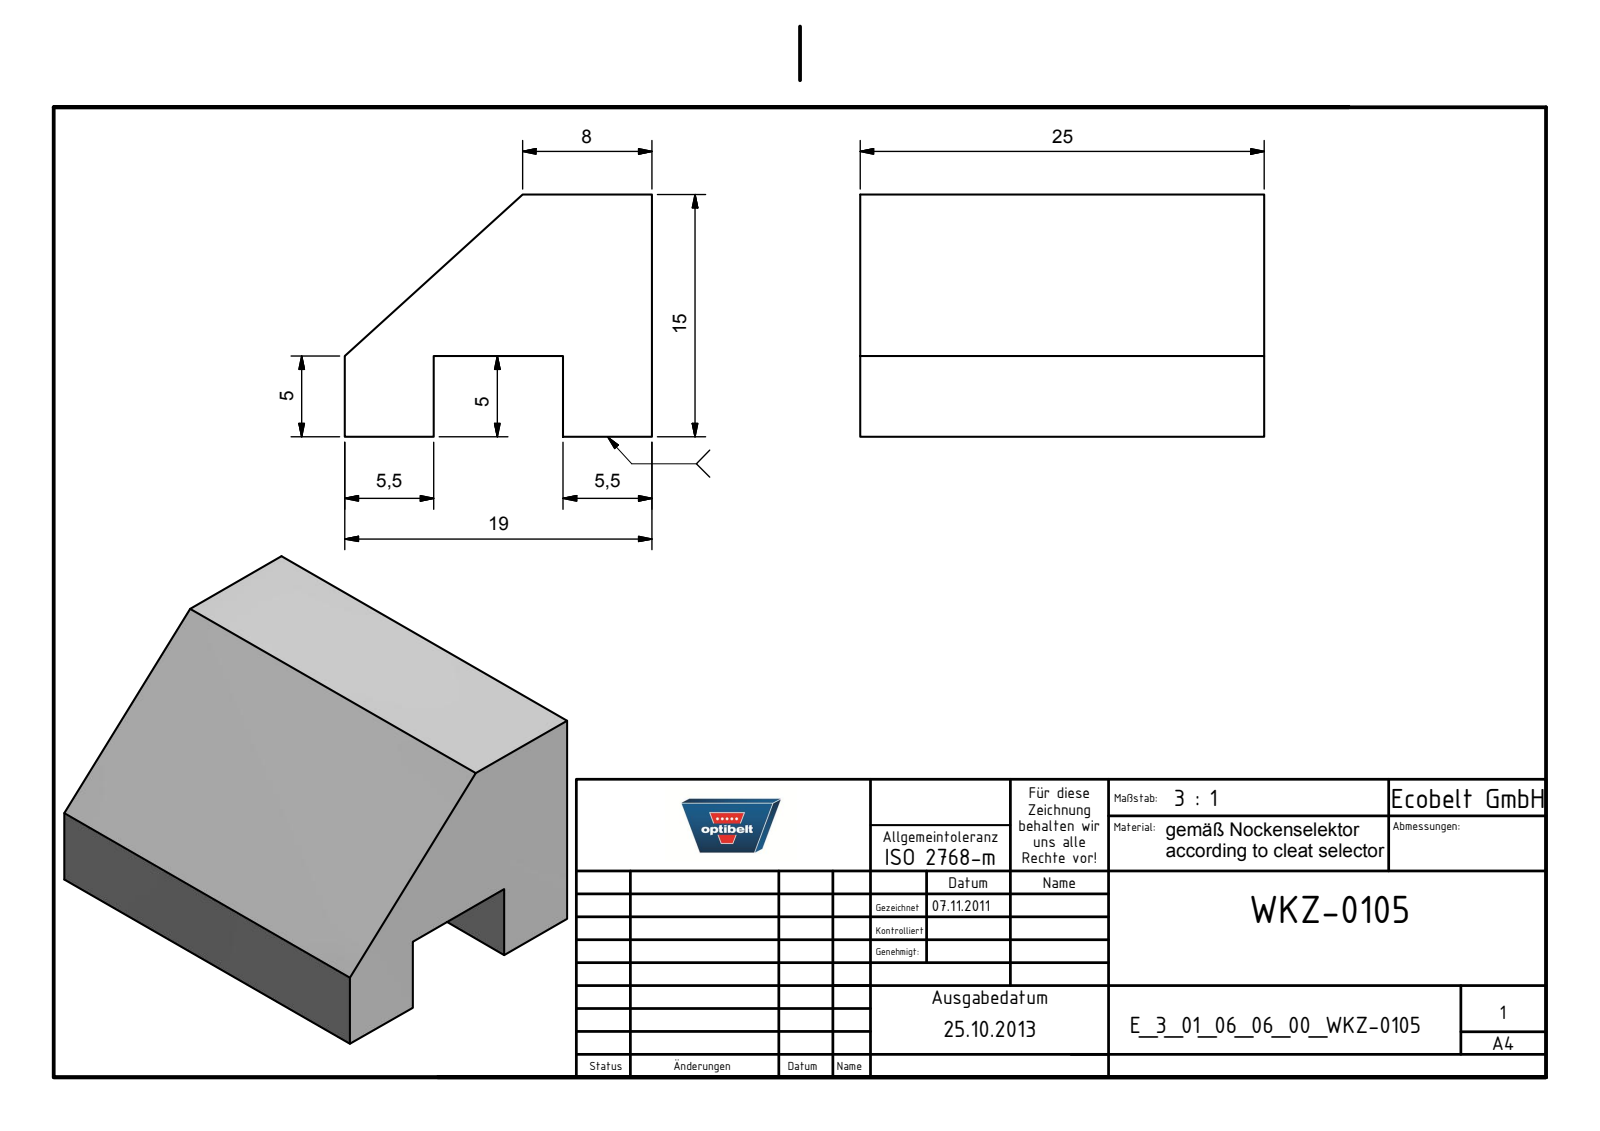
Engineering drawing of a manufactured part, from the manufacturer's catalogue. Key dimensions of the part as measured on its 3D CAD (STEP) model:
Part name (STEP PRODUCT): E_3_01_06_06_00_WKZ-0105
STEP written by: Autodesk Inventor 2025 (AUTOMOTIVE_DESIGN)
Units: millimetres
Bodies: 1 solid, 11 faces (11 planar, 0 cylindrical, 0 other)
Overall size (bounding box): 25 × 19 × 15
Volume: 4 750 mm³ · Surface area: 2 177 mm²
Main face-to-face distances: 5.5, 13.5, 5, 15, 10, 25, 19, 8
